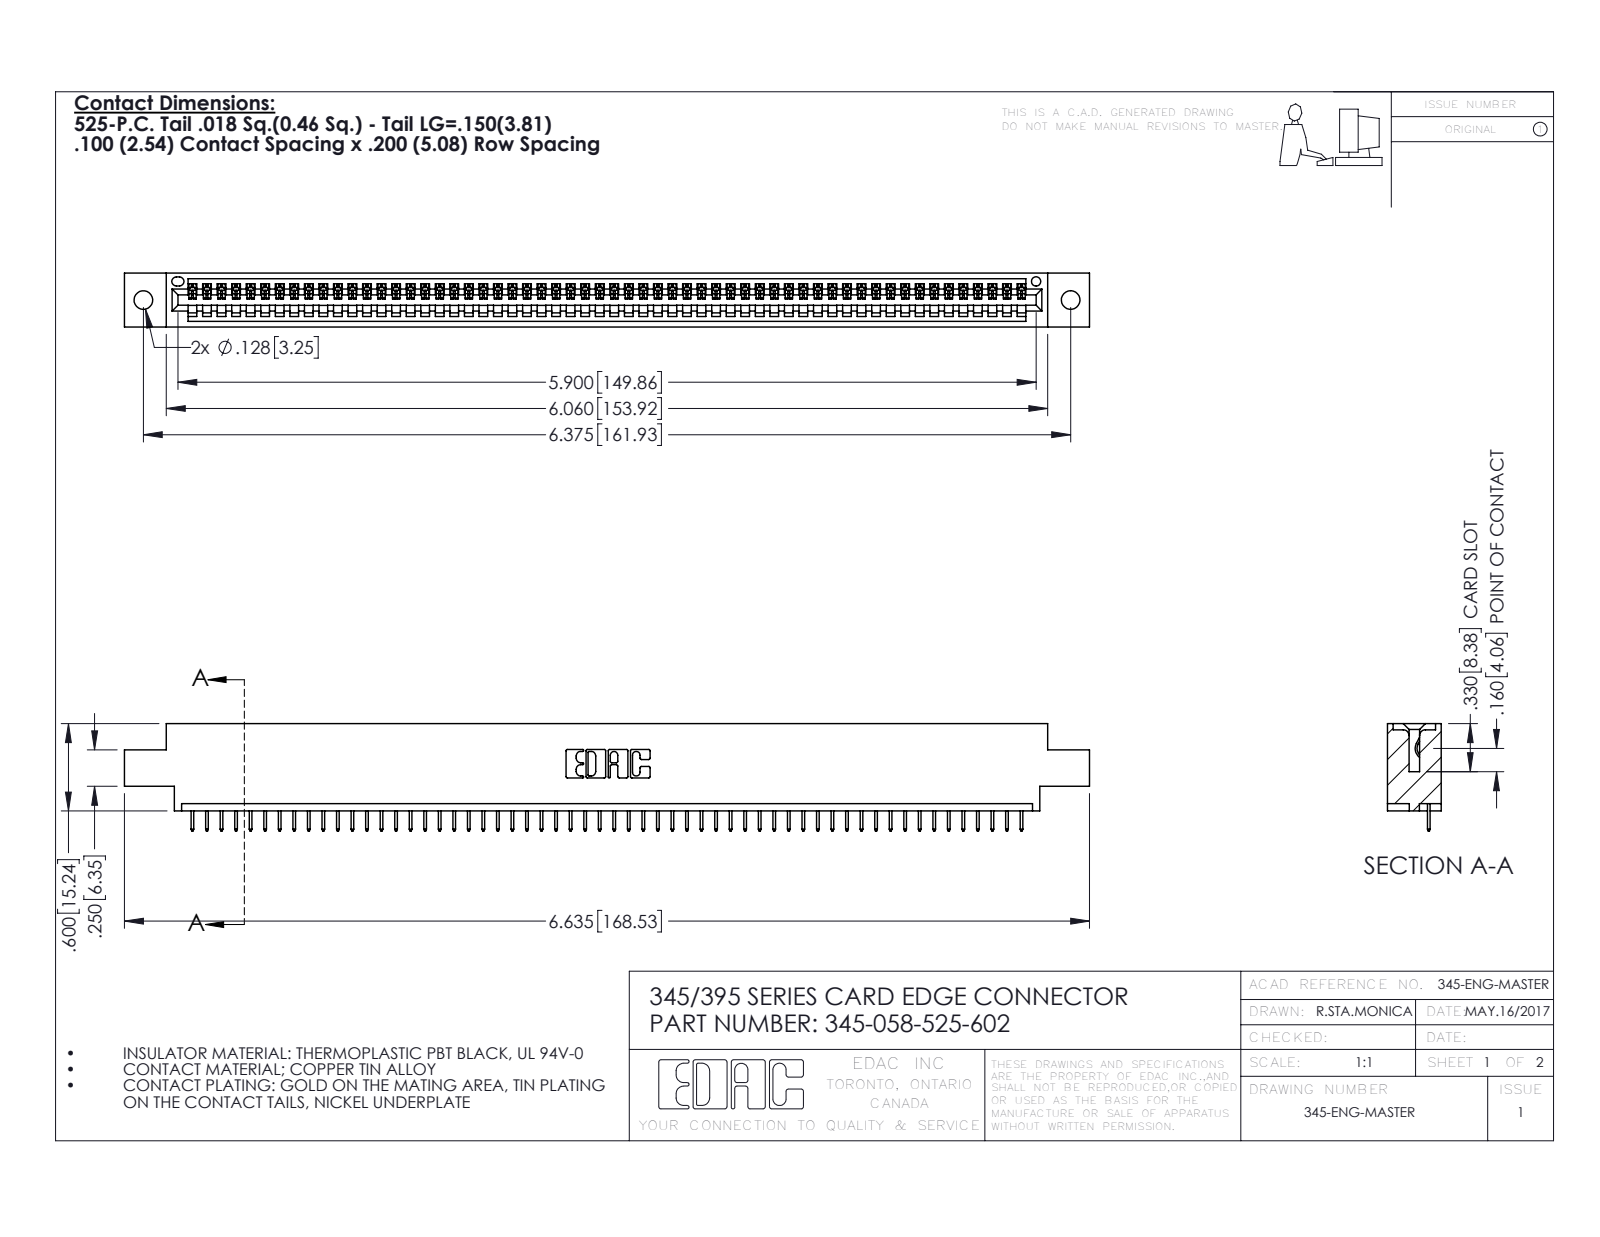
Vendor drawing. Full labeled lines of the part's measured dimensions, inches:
Part name (STEP PRODUCT): 345-058-525-602; 345 Part_0.170 Offset - 0.128 Dia; 345-292-001_345-293-125
STEP written by: SolidWorks 2020 (CONFIG_CONTROL_DESIGN)
Units: inches
Bodies: 59 solids, 3726 faces (2752 planar, 974 cylindrical, 0 other)
Overall size (bounding box): 6.635 × 0.737 × 0.37
Volume: 0.961 in³ · Surface area: 31.33 in²
Round holes (diameter × count): ⌀0.128 ×2, ⌀0.064 ×1
Partial cylindrical surfaces — rounded edges, fillets, slot ends (radius × count): R0.006 ×116, R0.01 ×22, R0.007 ×6, R0.031 ×6, R0.026 ×3, R0.031 ×2, R0.04 ×2, R0.014 ×1
Main face-to-face distances: 0.072, 0.298, 0.37, 0.2, 0.098, 0.272, 0.025, 0.225, 0.072, 0.175
Hole centre spacings: 0.27, 6.139, 6.375
